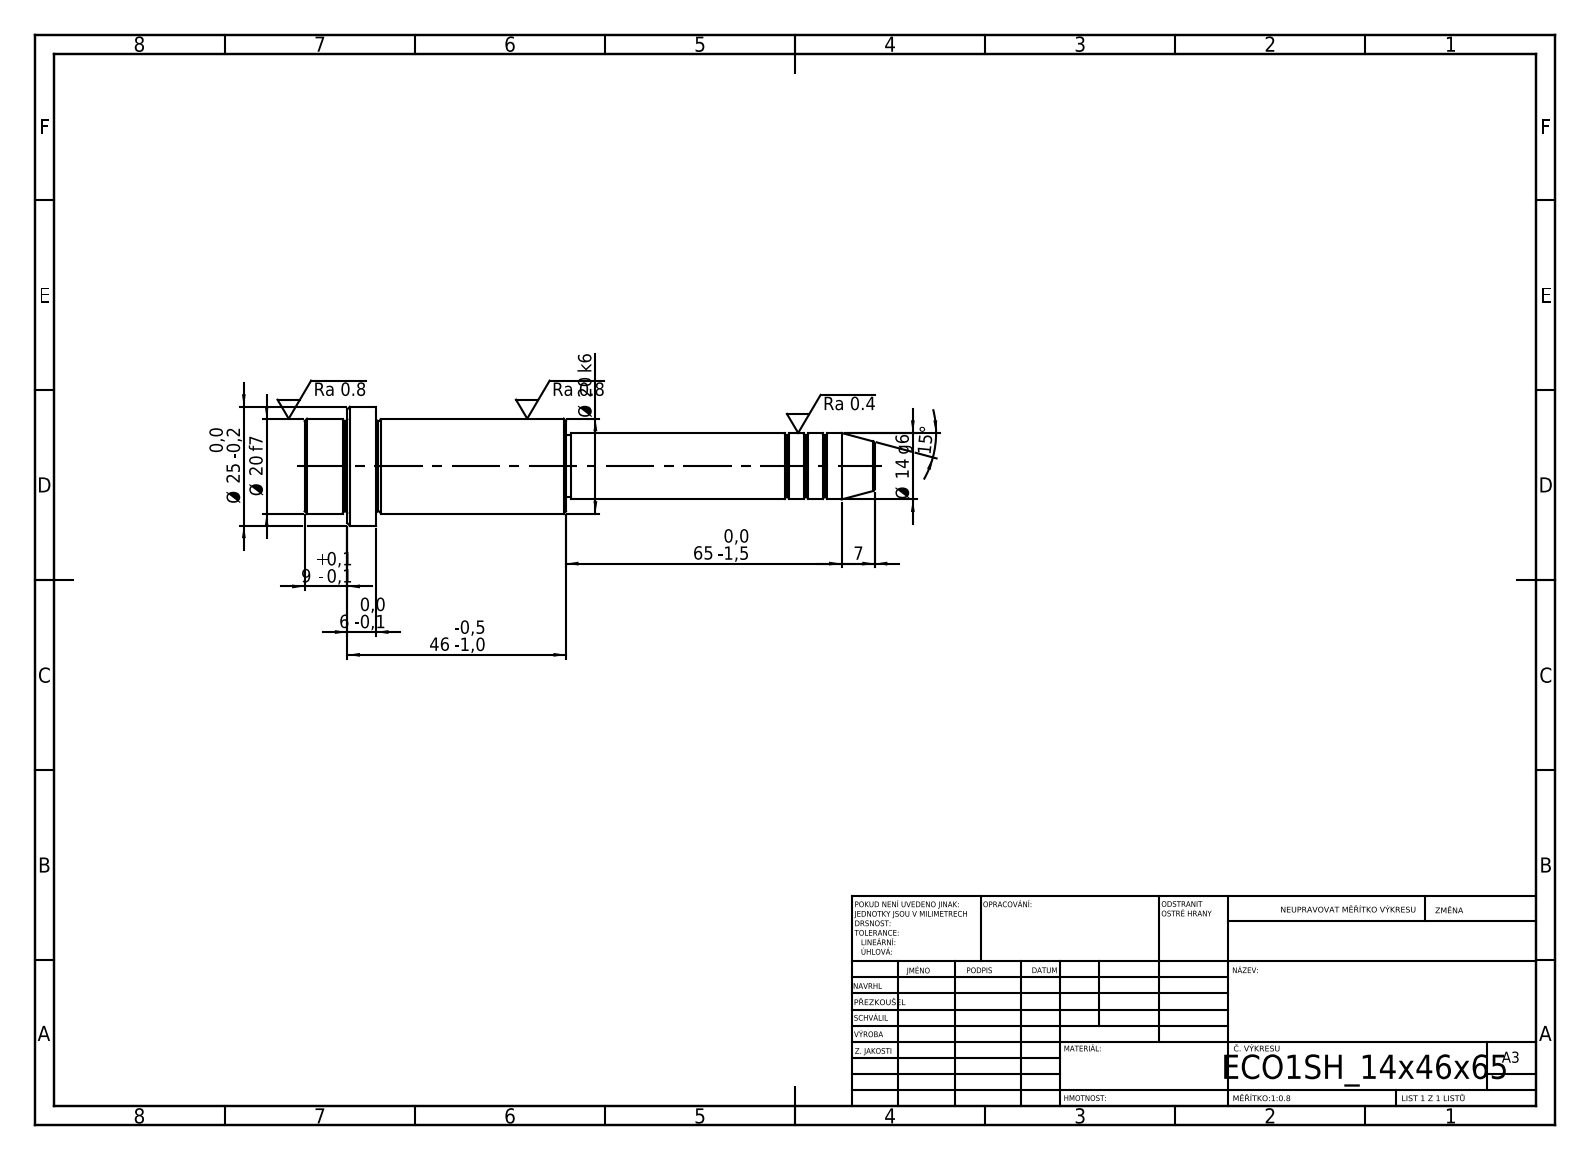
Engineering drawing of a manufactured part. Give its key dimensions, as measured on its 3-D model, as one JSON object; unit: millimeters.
{"step_written_by": "SolidWorks 2019 (CONFIG_CONTROL_DESIGN)", "units": "millimeters", "bodies": {"solids": 1, "faces": 52, "planar": 6, "cylindrical": 16, "other": 30}, "overall_size": [120, 25, 25], "volume_mm3": 27936, "surface_area_mm2": 7393, "round_bosses_or_shafts": [[25, 1], [20, 1], [14, 1], [13, 1]], "face_to_face_distances": [15, 40, 55, 46, 6, 9, 65, 105, 111, 120]}
